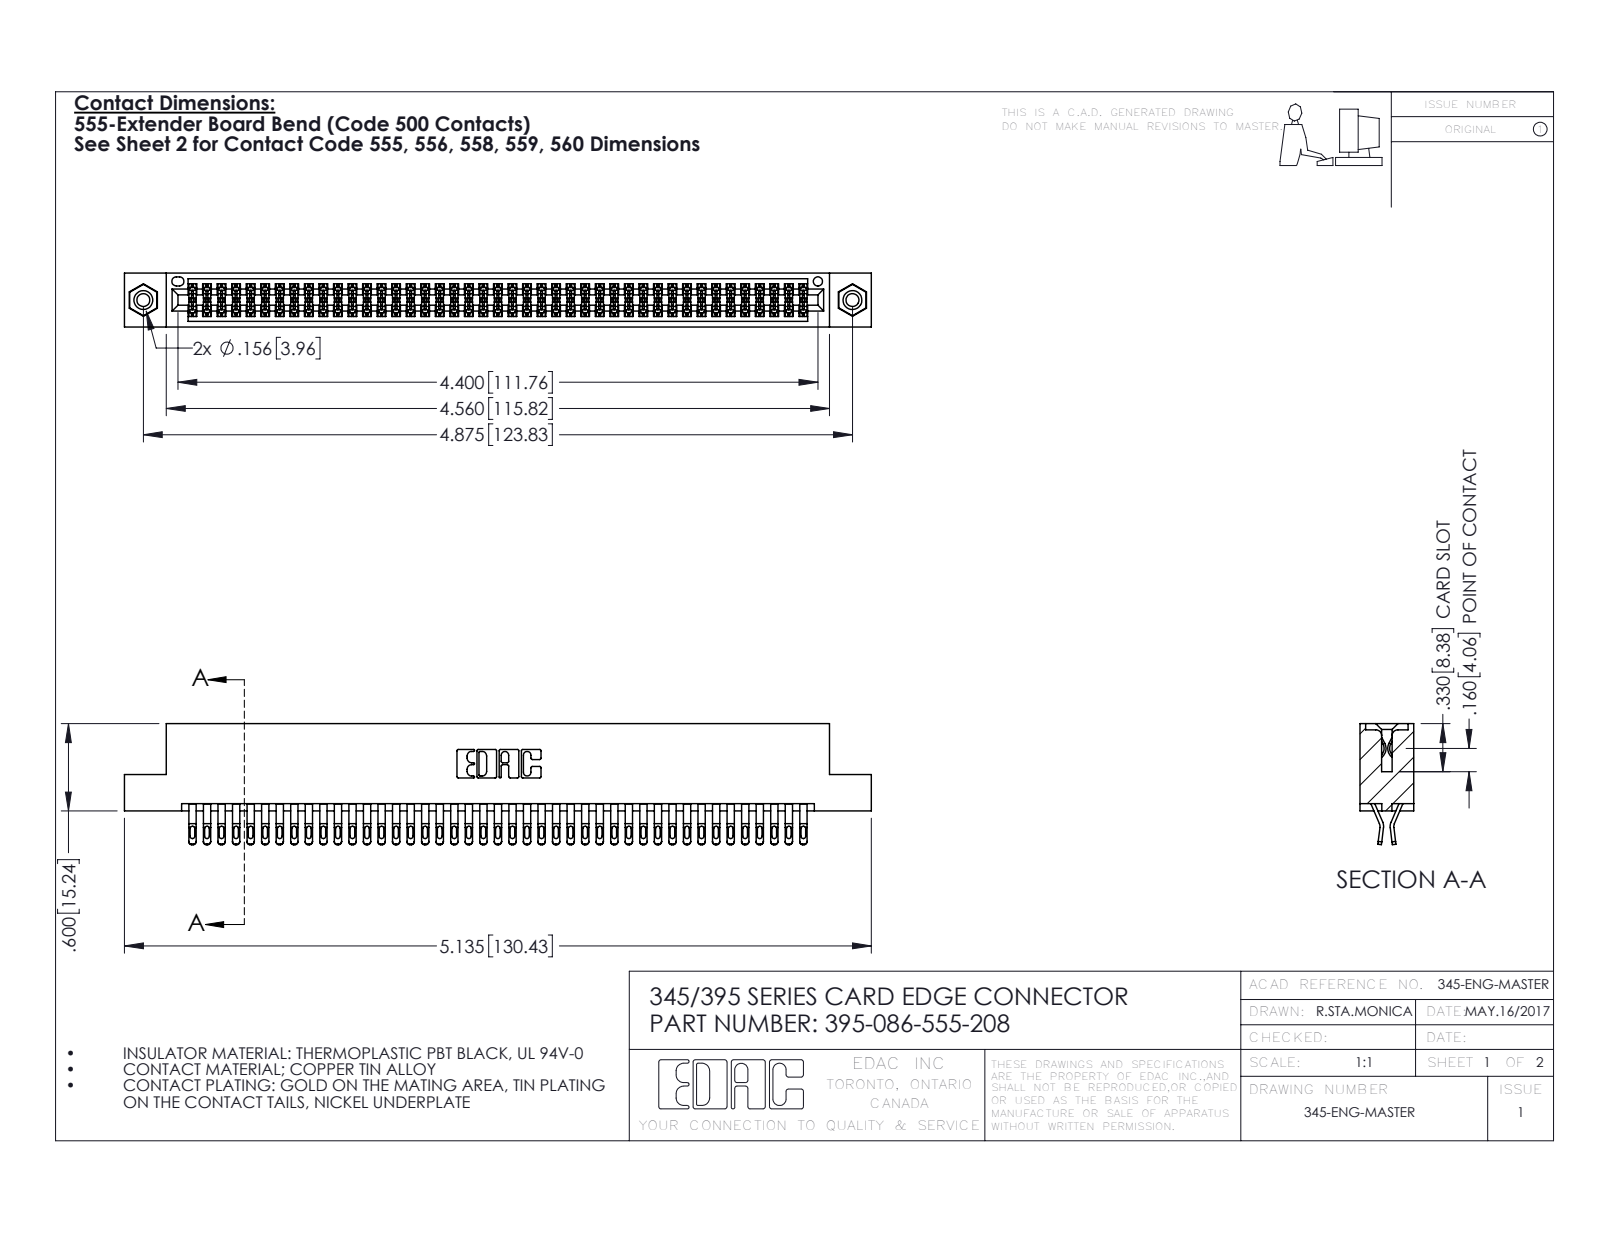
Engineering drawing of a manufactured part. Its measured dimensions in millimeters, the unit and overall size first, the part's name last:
Units: millimetres
Overall size (bounding box): 130.4 × 21.1 × 9.4
Round holes (diameter × count): ⌀2.3 ×2, ⌀3.2 ×2, ⌀4 ×2, ⌀1.6 ×1
Round bosses / shafts (diameter × count): ⌀3.9 ×2
Partial cylindrical surfaces — rounded edges, fillets, slot ends (radius × count): R0.4 ×215, R0.5 ×172, R0.2 ×129, R0.3 ×22, R0.2 ×6, R0.8 ×6, R0.7 ×3, R0.3 ×2
Main face-to-face distances: 1.8, 7.6, 0.6, 9.4, 5.1, 2.5, 6.9, 5.7, 4.4, 3.8
Hole centre spacings: 6.9, 117.8, 123.8
Volume: 12 900 mm³ · Surface area: 20 000 mm²
Bodies: 89 solids, 5002 faces (2778 planar, 2208 cylindrical, 16 other)
Part name (STEP PRODUCT): 345-250-001_345-250-003-102; 395-086-555-208; 345-292-001_555 Tail; 345 Part_Flush Mounting Lugs - 0.156 Dia-TI
STEP written by: SolidWorks 2016 (CONFIG_CONTROL_DESIGN)
